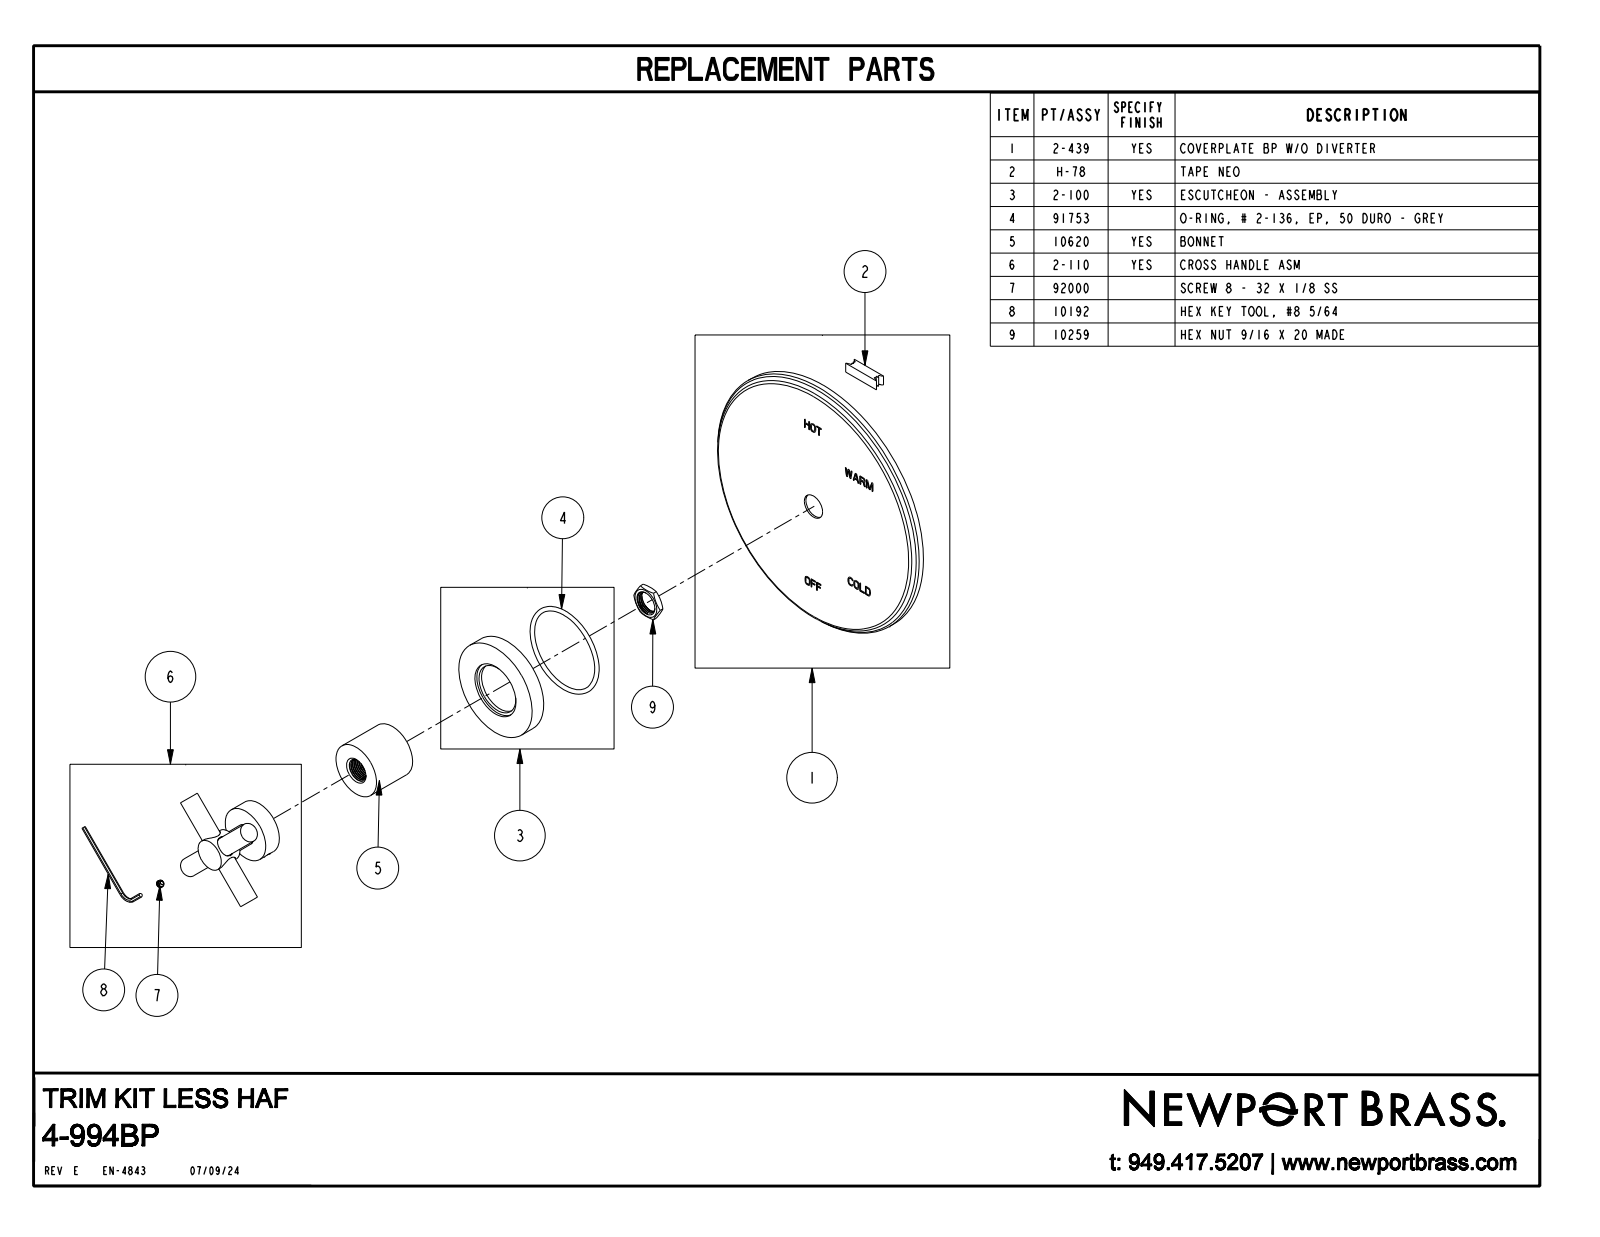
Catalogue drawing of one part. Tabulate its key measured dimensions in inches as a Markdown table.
| quantity | value |
| --- | --- |
| part name | 4-994BP |
| STEP written by | CREO PARAMETRIC BY PTC INC, 2018400 (CONFIG_CONTROL_DESIGN) |
| units | inches |
| bodies | 1 solid, 379 faces (343 planar, 30 cylindrical, 6 other) |
| overall size | 6.5 × 6.5 × 3.416 |
| volume | 14.91 in³ |
| surface area | 91.99 in² |
| round holes (diameter × count) | 0.47 × 2 |
| round bosses / shafts (diameter × count) | 0.445 × 4, 6.5 × 1, 2.375 × 1, 1.313 × 1, 0.75 × 1, 0.5 × 1, 0.4 × 1 |
| main face-to-face distances | 0.313, 0.688, 0.375, 0.02, 1.503, 1.796, 1.816, 1.483, 1.108, 1.128 |
